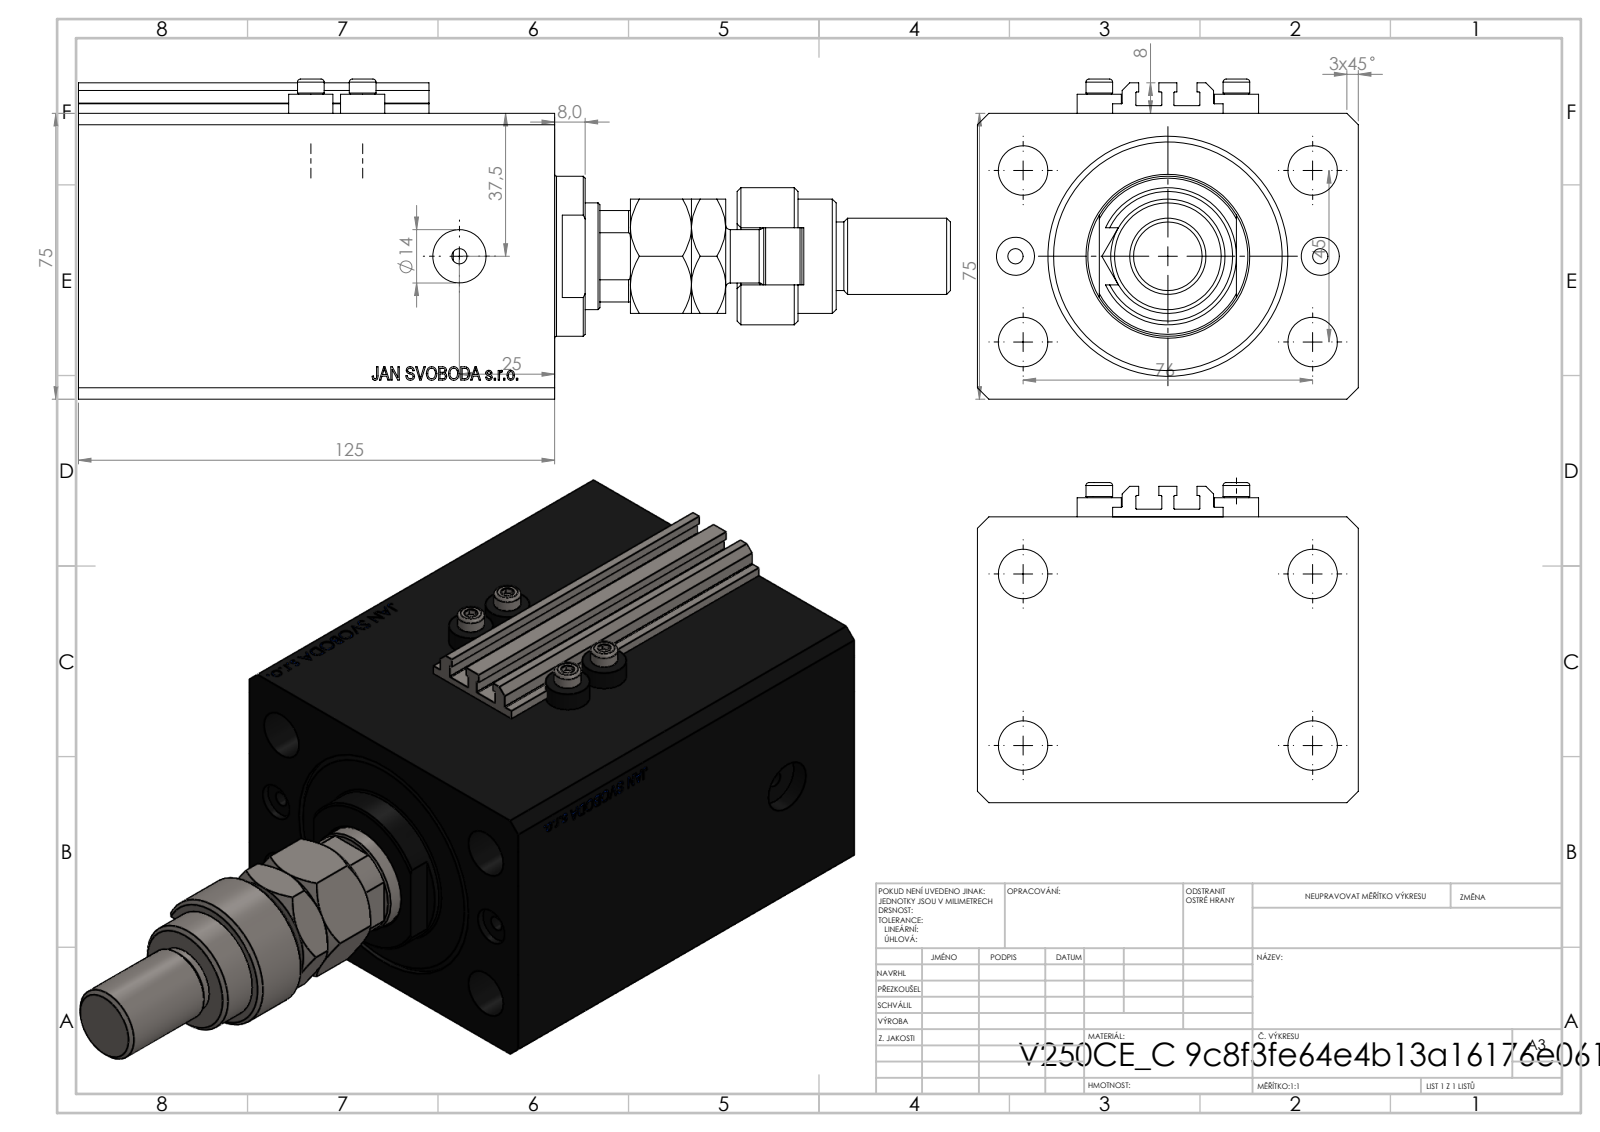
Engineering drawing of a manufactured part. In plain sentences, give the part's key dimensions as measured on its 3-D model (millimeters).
The part is named "V250CE_C_Body; ALLEN BOLT V250CE; MFA; V250CE_VC_C (+2 more)". Its 3-D file was written by "SolidWorks 2019 (CONFIG_CONTROL_DESIGN)". It is 10 solids with 1119 faces: 532 planar, 99 cylindrical and 488 other. Overall it measures 228.9 by 100 by 84 millimeters. Its volume is 868 816 cubic millimeters and its surface area 157 525 square millimeters. Round holes: 8 of diameter 4, 4 of diameter 13, 2 of diameter 10, 2 of diameter 14, 1 of diameter 18.5, 1 of diameter 28, 1 of diameter 50, 1 of diameter 63. Round bosses or shafts: 4 of diameter 11.6, 4 of diameter 7, 1 of diameter 42, 1 of diameter 36, 1 of diameter 30, 1 of diameter 22, 1 of diameter 20, 1 of diameter 18. Partial cylindrical surfaces (rounded edges, fillets, slot ends): 10 of radius 0.2, 1 of radius 7.5, 1 of radius 12, 1 of radius 13.5. The main face-to-face distances are 75, 100, 125, 11.9, 113.1, 98.4, 86.5, 26.6, 30, 48.4. The hole center spacings are 22.59, 44.16, 81.18, 13.6, 36, 38.48, 40, 45.
